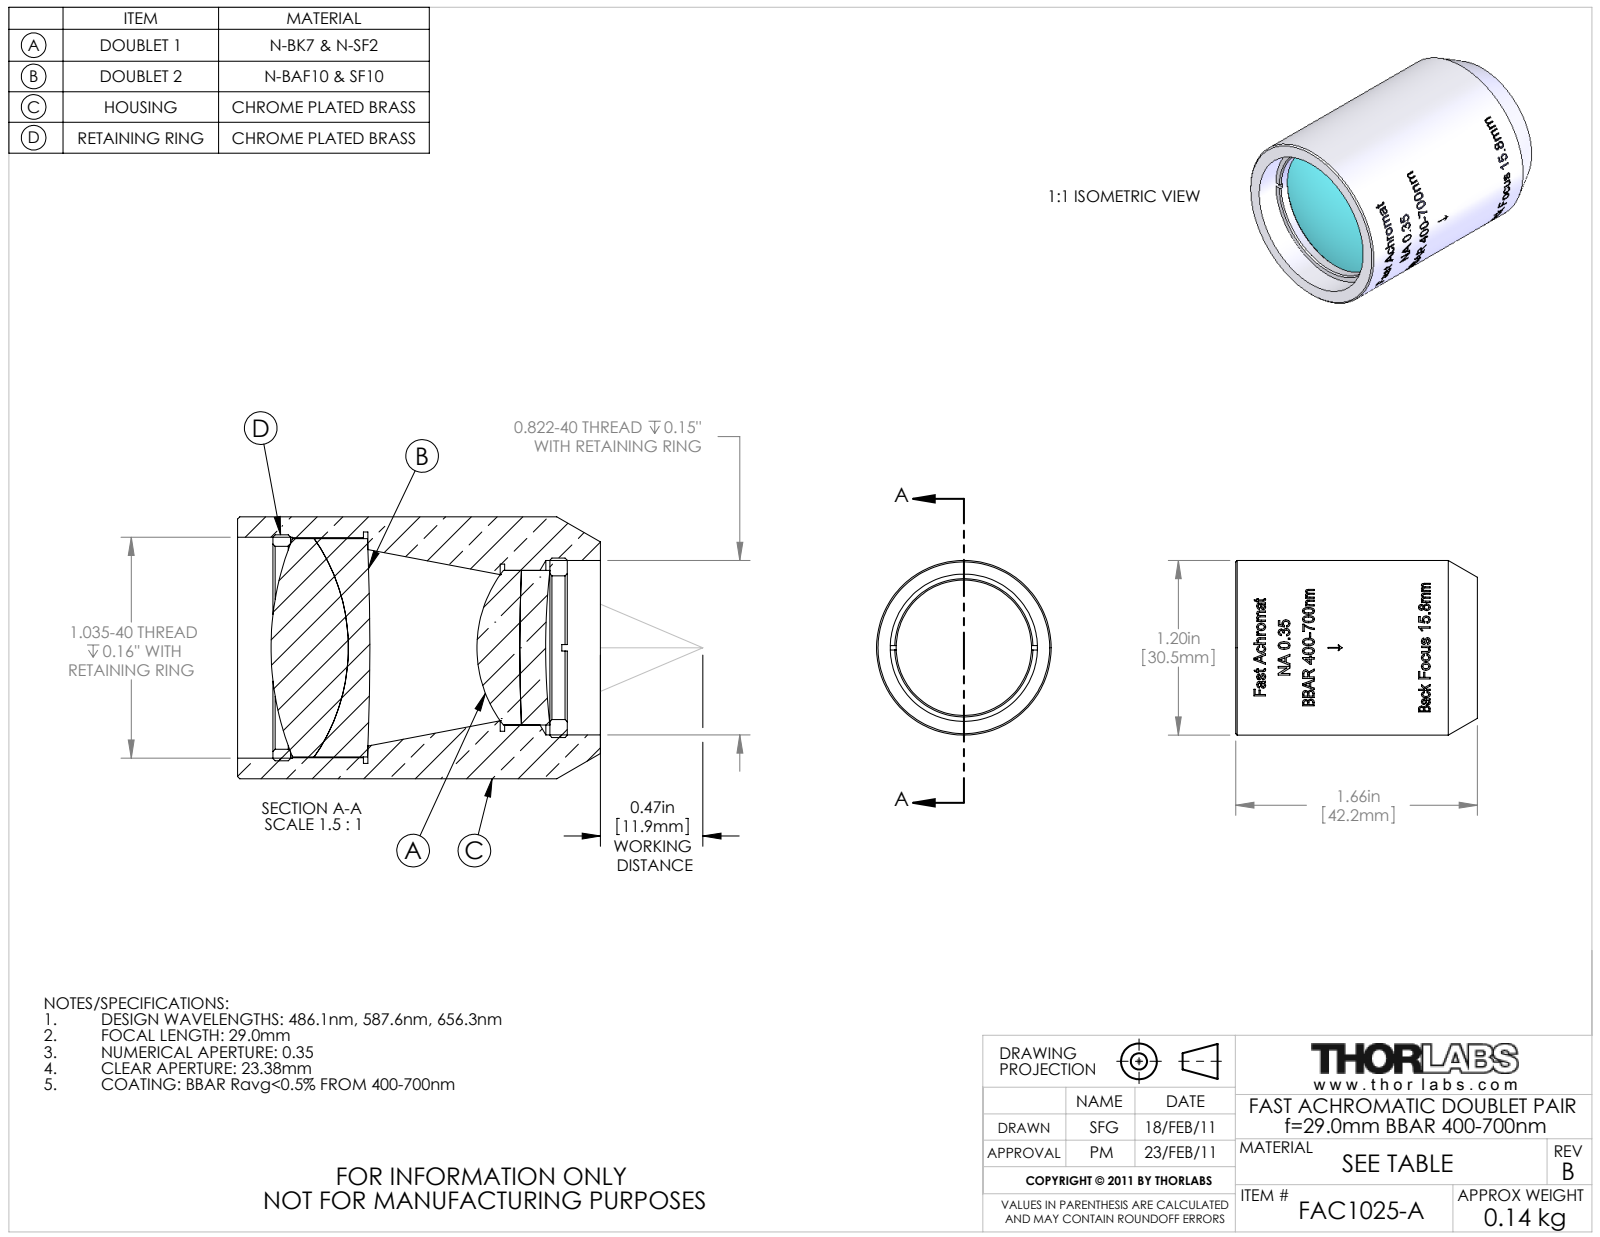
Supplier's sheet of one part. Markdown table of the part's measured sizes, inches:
| quantity | value |
| --- | --- |
| part name | 20560-E0W |
| STEP written by | SolidWorks 2009 (AUTOMOTIVE_DESIGN) |
| units | inches |
| bodies | 7 solids, 201 faces (24 planar, 135 cylindrical, 42 other) |
| overall size | 1.662 × 1.2 × 1.2 |
| volume | 1.298 in³ |
| surface area | 19.89 in² |
| round holes (diameter × count) | 0.659 × 1, 0.669 × 1, 0.766 × 1, 0.799 × 1, 0.93 × 1, 1.008 × 1, 1.012 × 1, 1.06 × 1 |
| round bosses / shafts (diameter × count) | 1.2 × 1, 1.035 × 1, 1 × 1, 0.822 × 1, 0.709 × 1 |
| main face-to-face distances | 0.597, 1.065, 1.662, 0.02, 0.626, 0.231, 0.834, 1.431, 0.151, 0.08 |
